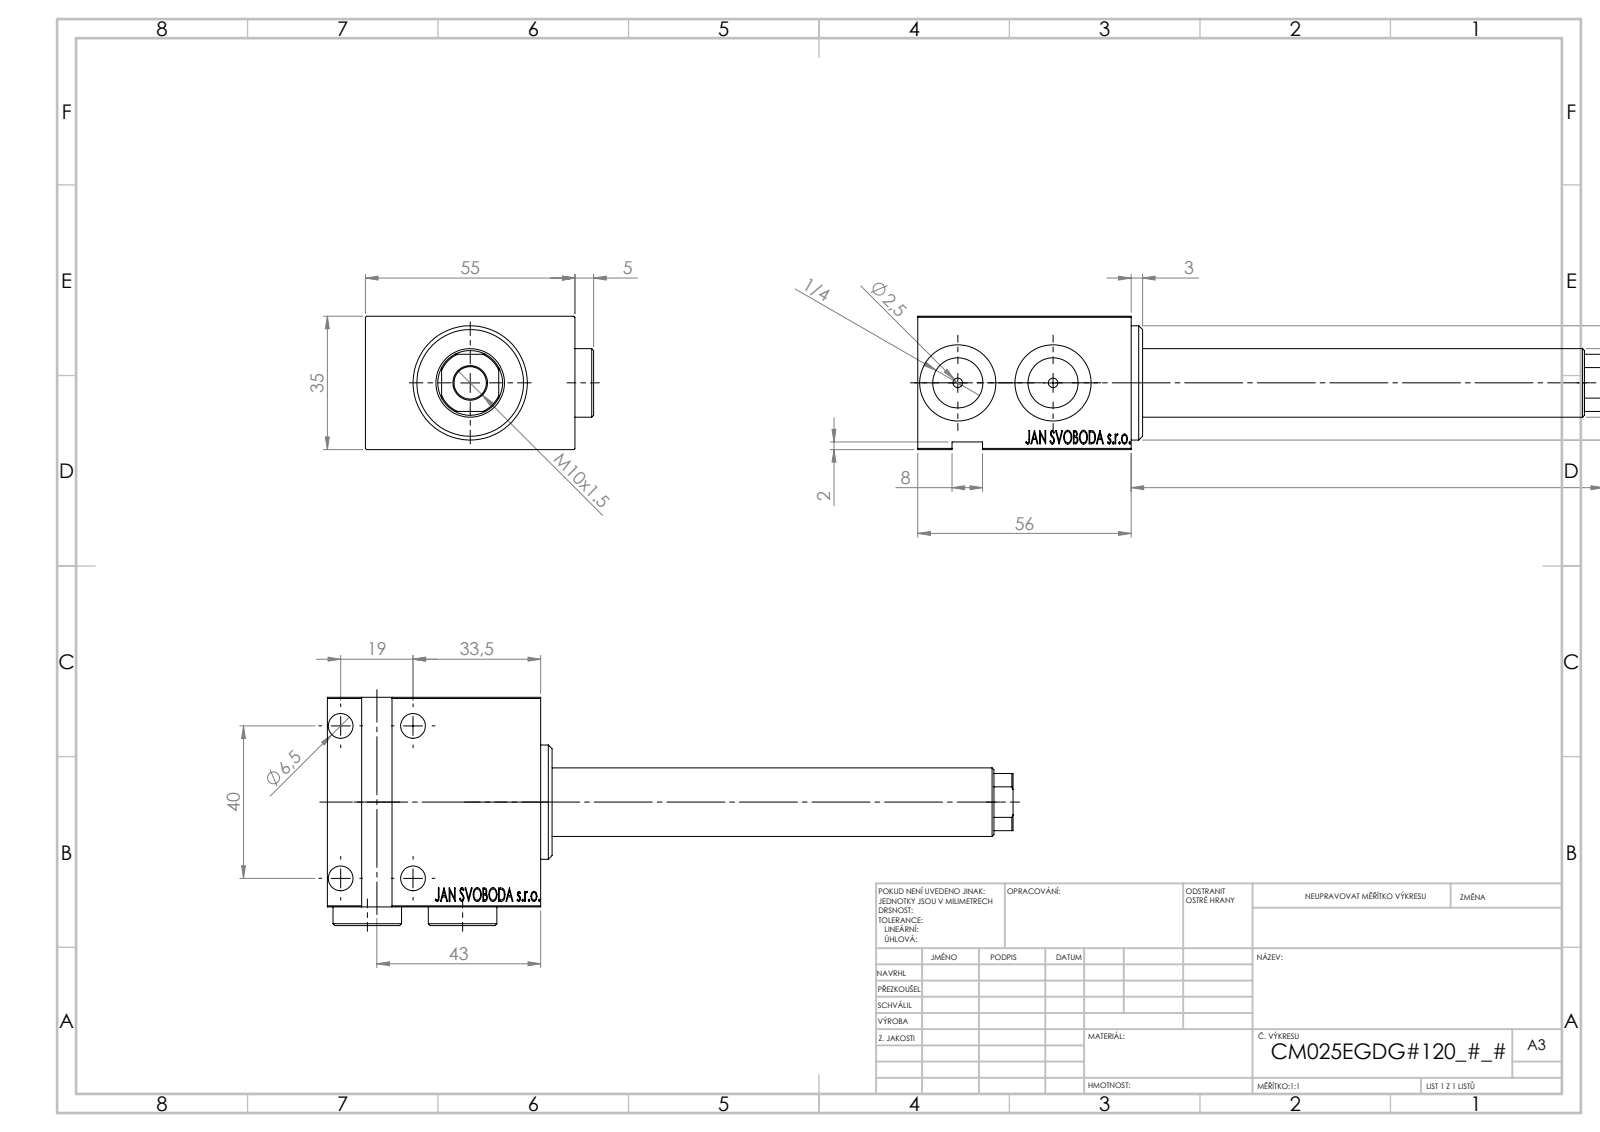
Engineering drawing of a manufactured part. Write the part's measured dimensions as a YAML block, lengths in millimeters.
part_name: "Zatka_OIL_PORT; V450CM_VC_B; V450CM_E_VCP; V450CM_E_Body"
step_written_by: "SolidWorks 2019 (CONFIG_CONTROL_DESIGN)"
units: millimeters
bodies: {solids: 5, faces: 903, planar: 441, cylindrical: 64, other: 398}
overall_size: [180, 59.9, 35]
volume: 128278
surface_area: 40125
round_holes:
  - {diameter: 6.5, count: 4}
  - {diameter: 2.5, count: 2}
  - {diameter: 10.5, count: 2}
  - {diameter: 13.16, count: 2}
  - {diameter: 20, count: 2}
  - {diameter: 8.5, count: 1}
  - {diameter: 18, count: 1}
  - {diameter: 25, count: 1}
round_bosses_or_shafts:
  - {diameter: 18, count: 2}
  - {diameter: 30, count: 1}
  - {diameter: 27, count: 1}
partial_cylinders:
  - {radius: 5.25, count: 2}
  - {radius: 8.5, count: 1}
face_to_face_distances: [35, 56, 5, 55, 54.9, 51, 33, 2, 3, 54.8]
hole_center_spacings: [19, 40, 44.28, 25]
